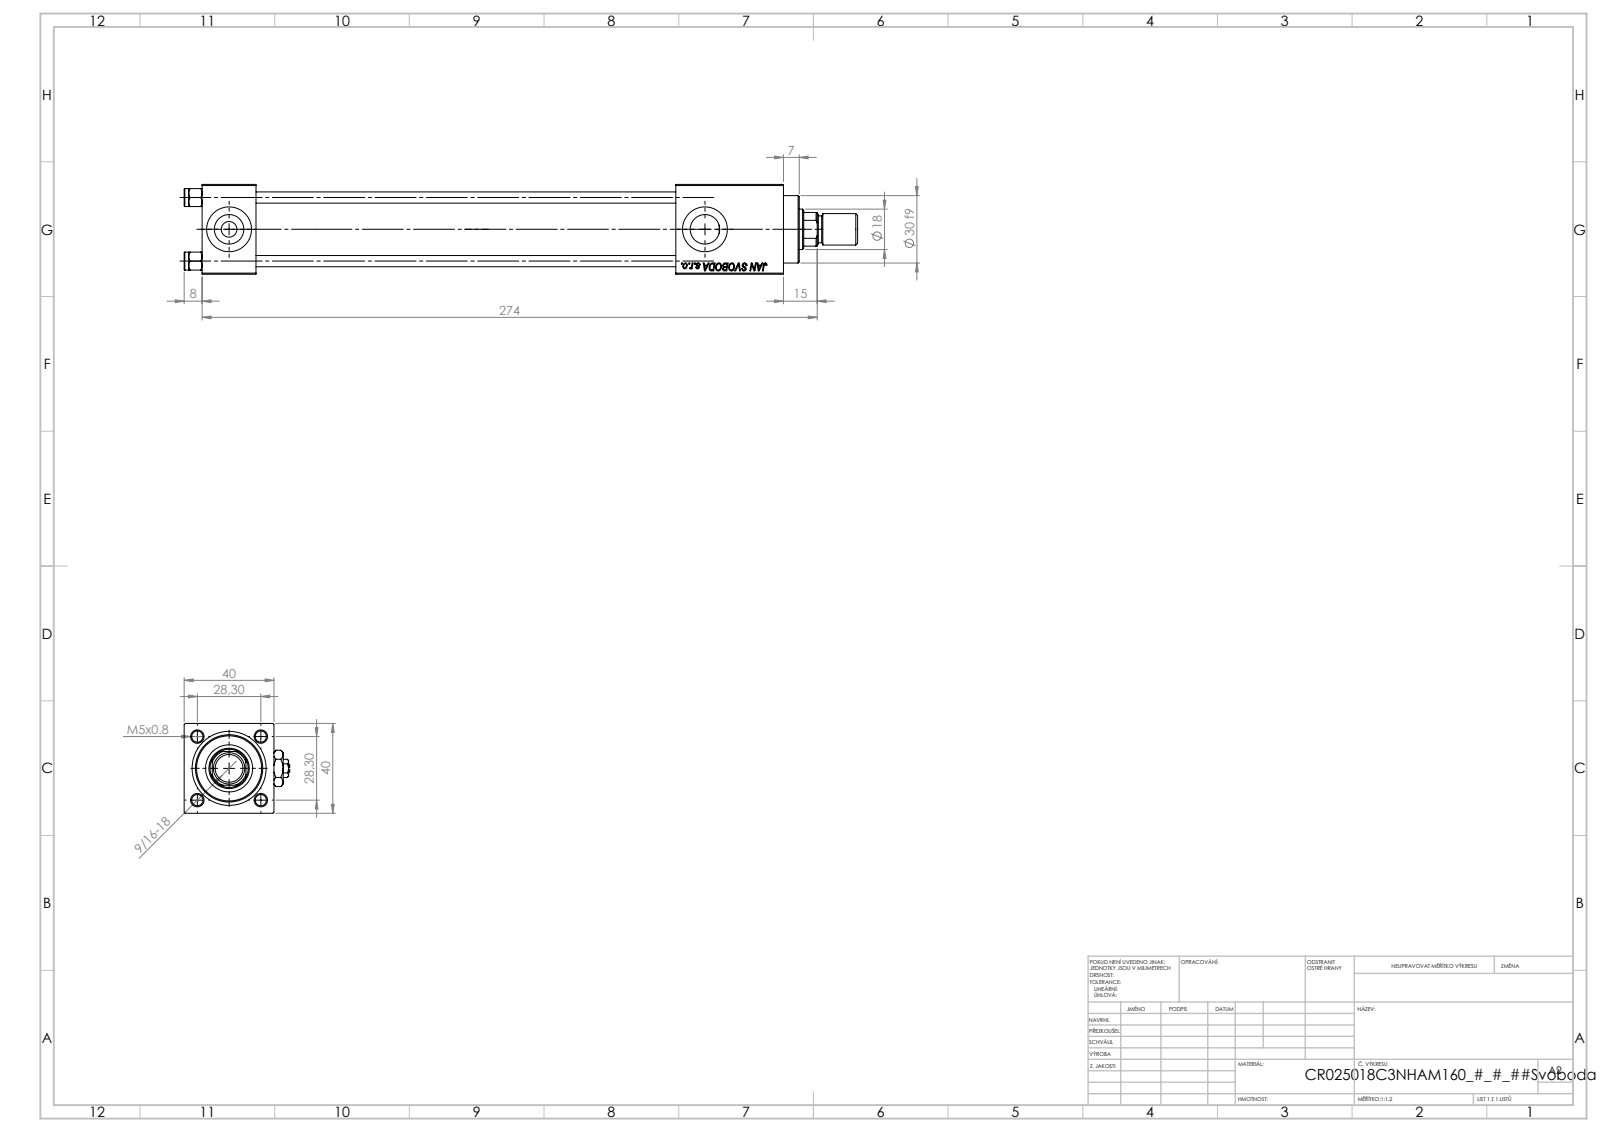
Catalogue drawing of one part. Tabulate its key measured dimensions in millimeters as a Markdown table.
| quantity | value |
| --- | --- |
| part name | Zatka_pro_OIL_PORT; V215_VC_A; V215CR_C_Body; NUT_M5_C (+3 more) |
| STEP written by | SolidWorks 2019 (CONFIG_CONTROL_DESIGN) |
| units | millimeters |
| bodies | 14 solids, 1259 faces (575 planar, 100 cylindrical, 584 other) |
| overall size | 300 × 47 × 40 |
| volume | 234 831 mm³ |
| surface area | 100 954 mm² |
| round holes (diameter × count) | 5 × 4, 20 × 3, 7 × 2, 13.16 × 2, 8.5 × 1, 18 × 1, 21 × 1, 25 × 1, 30 × 1 |
| round bosses / shafts (diameter × count) | 8 × 4, 31 × 1, 14 × 1, 12 × 1 |
| partial cylindrical surfaces (radius × count) | 8.5 × 1 |
| main face-to-face distances | 40, 24, 39.8, 211, 187, 230.3, 206.3, 19.3, 48, 8 |
| hole center spacings | 20.01, 28.3, 40.02, 212 |
